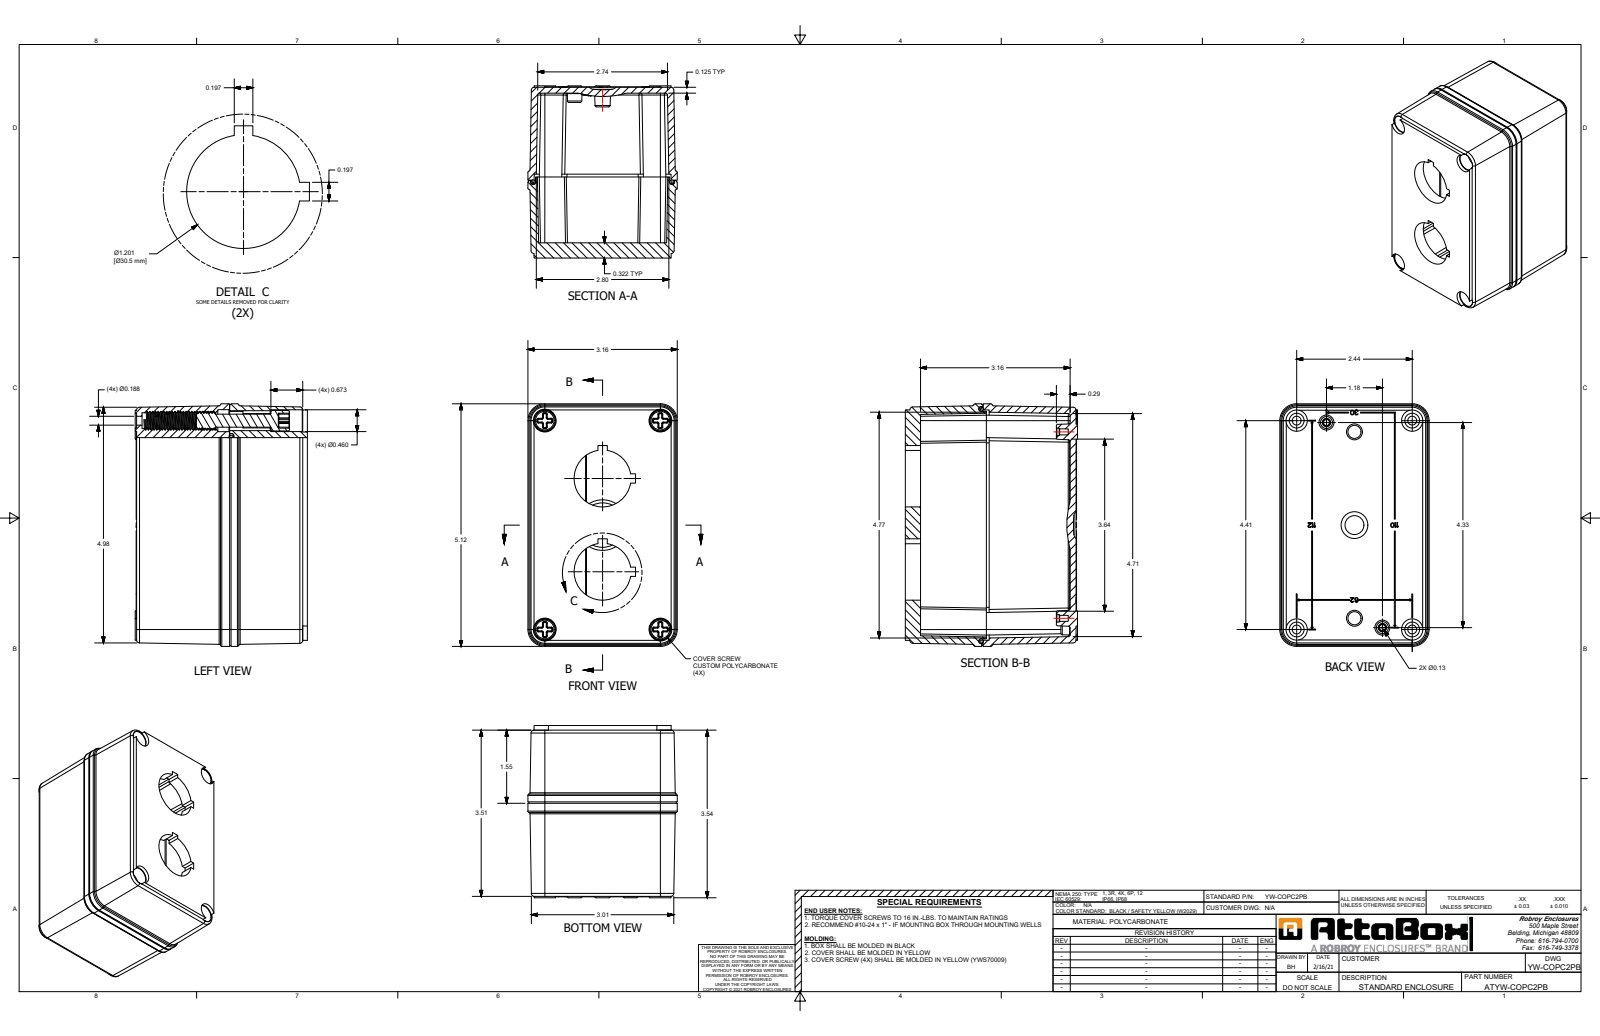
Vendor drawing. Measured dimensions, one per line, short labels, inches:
name: YW-COPC2PB
written by: SolidWorks 2023 (AUTOMOTIVE_DESIGN)
unit: in
bodies: 7 solids, 935 faces (280 planar, 377 cylindrical, 278 other)
size: 5.124 × 3.637 × 3.155
volume: 15.44 in³; area: 198.2 in²
holes: 6× ⌀0.1, 4× ⌀0.157, 4× ⌀0.187, 4× ⌀0.313, 4× ⌀0.329, 4× ⌀0.46, 4× ⌀0.465, 2× ⌀0.126, 2× ⌀0.127, 2× ⌀1.201
bosses: 4× ⌀0.45, 4× ⌀0.433, 4× ⌀0.276, 2× ⌀0.1
rounds: 50× R0.02, 32× R0.01, 16× R0.015, 16× R0.03, 16× R0.04, 11× R0.063, 8× R0.08, 8× R0.11
face distances: 0.135, 0.161, 3.075, 2.94, 3.607, 0.125, 3.482, 2.914, 2.779, 3.285
hole spacings: 1.243, 4.348, 0.57, 0.622, 0.631, 1.726, 1.726, 1.811
